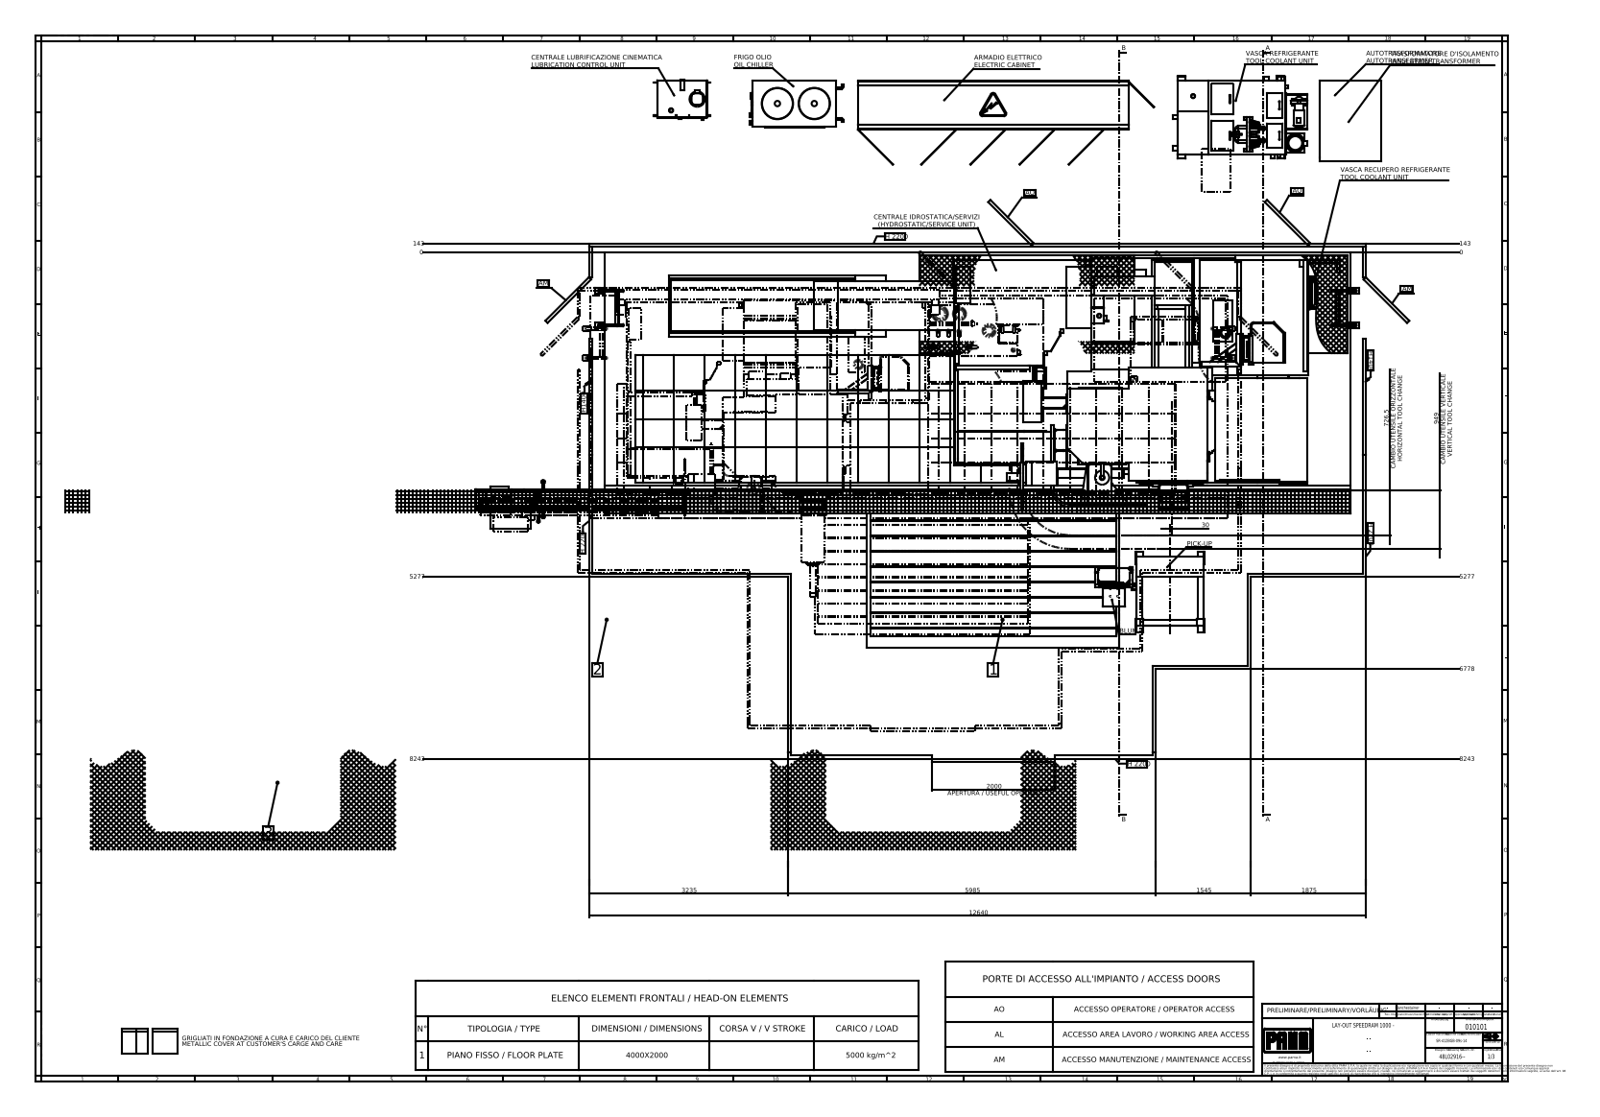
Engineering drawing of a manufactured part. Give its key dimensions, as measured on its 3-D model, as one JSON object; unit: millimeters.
{"part_name": "S000047; S003192_X=MIN; Y=MIN; Z=MIN; W=MIN; S002727_INTERASSE=1000; S001573 (+8 more)", "step_written_by": "SolidWorks 2023 (AUTOMOTIVE_DESIGN)", "units": "millimeters", "bodies": {"solids": 398, "faces": 6368, "planar": 4467, "cylindrical": 1438, "other": 463}, "overall_size": [16140, 14057.4, 7912.5], "volume_mm3": 415400000000, "surface_area_mm2": 1633000000, "round_holes": [[35, 64], [69.6, 63], [37.2, 18], [30, 9], [13, 8], [14, 8], [8, 6], [12.5, 4], [56.66, 4], [60, 4], [25.6, 3], [50, 3]], "round_bosses_or_shafts": [[42.4, 18], [20, 14], [40, 11], [9, 10], [55, 8], [66.3, 7], [60, 6], [35, 6]], "partial_cylinders_radius": [[5, 128], [15, 53], [8, 52], [35, 26], [6, 25], [3, 21], [4, 21], [10, 20]], "face_to_face_distances": [2000, 50, 1247, 753, 5, 13986, 10, 16140, 2650, 2700], "hole_center_spacings": [273.13, 500, 1235.56, 758.02, 1423.59, 1000, 130, 260]}
